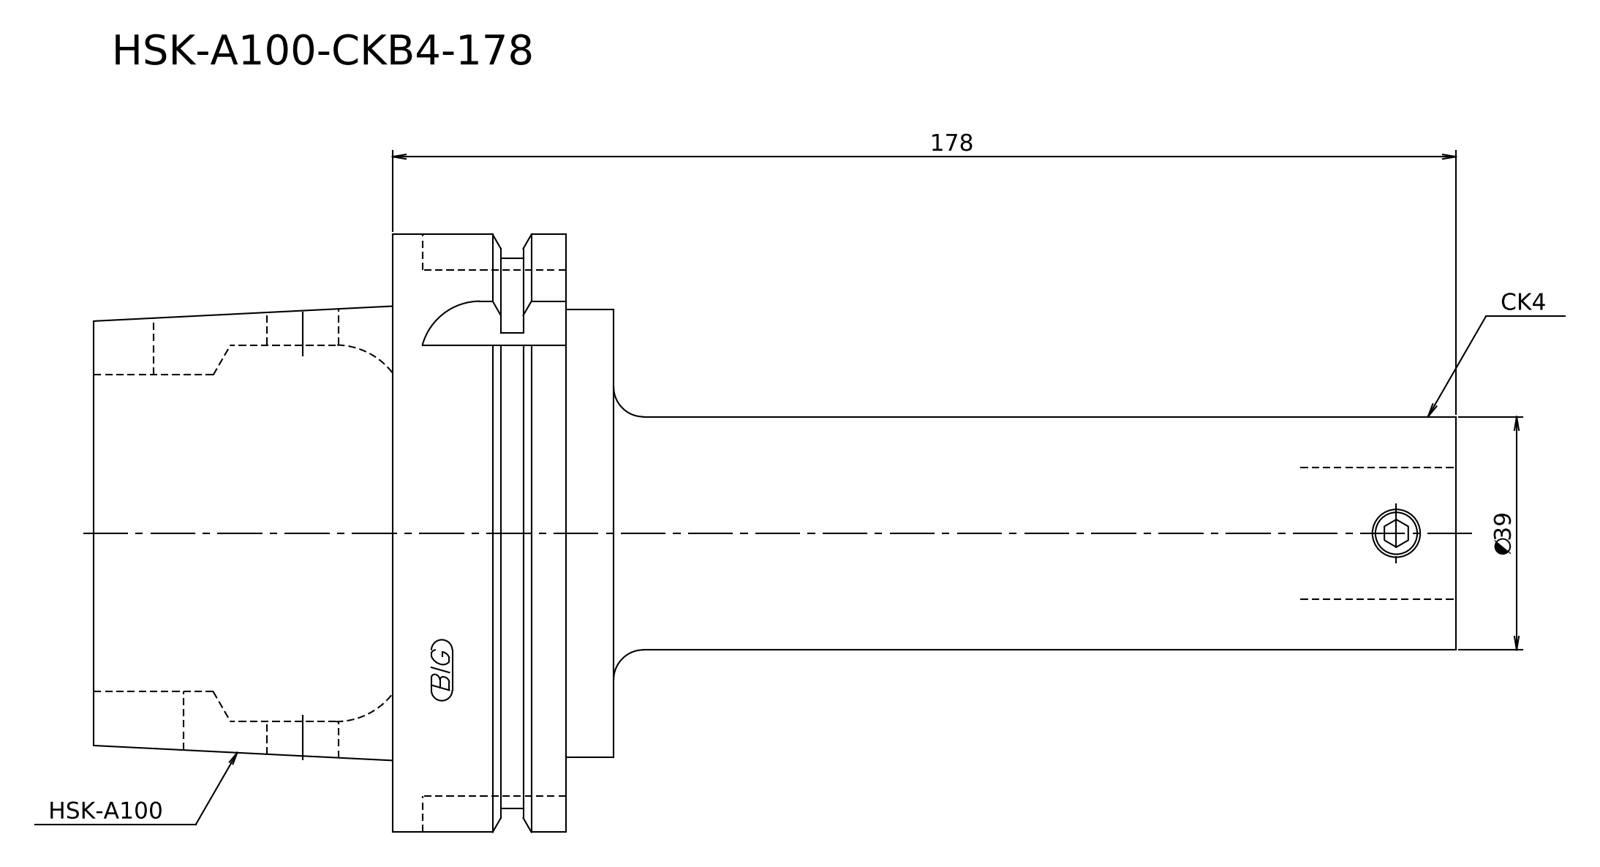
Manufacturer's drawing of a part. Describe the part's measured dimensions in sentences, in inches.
Its 3-D file was written by "Kubotek KeyCreator V8.5.1 (14335) (CONFIG_CONTROL_DESIGN)". It is 1 solid with 17 faces: 7 planar, 6 cylindrical and 4 other. Overall it measures 8.976 by 3.937 by 3.937 inches. Its volume is 39.05 cubic inches and its surface area 87.33 square inches. Round bosses or shafts: 1 of diameter 3.937, 1 of diameter 3.622, 1 of diameter 2.984, 1 of diameter 2.953, 1 of diameter 1.535. The main face-to-face distances are 3.11, 1.142, 1.969, 0.315, 1.457, 3.425, 5.551, 5.866, 7.008, 8.976.
